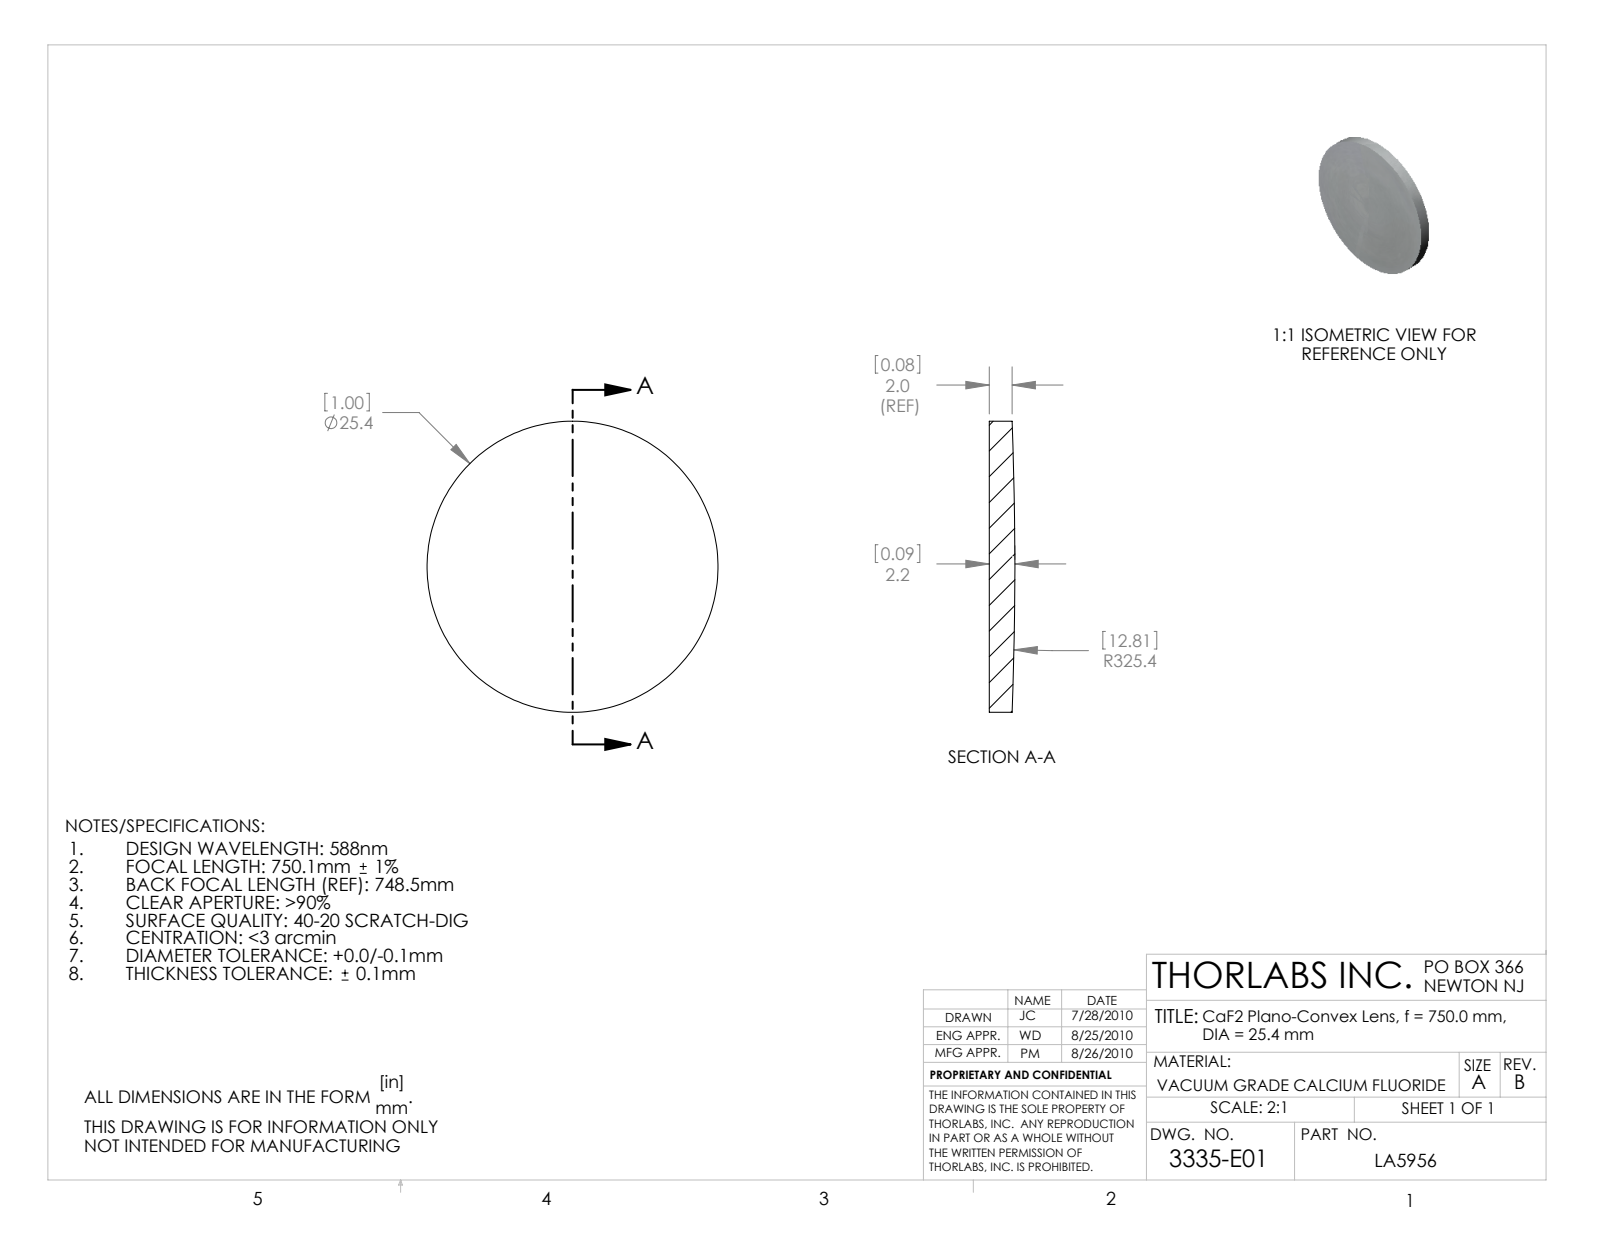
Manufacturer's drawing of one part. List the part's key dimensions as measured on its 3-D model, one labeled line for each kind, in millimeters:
Part name (STEP PRODUCT): 3335-E0W
STEP written by: SolidWorks 2009 (AUTOMOTIVE_DESIGN)
Units: millimetres
Bodies: 1 solid, 5 faces (1 planar, 2 cylindrical, 2 other)
Overall size (bounding box): 25.4 × 25.4 × 2.2
Volume: 1 100 mm³ · Surface area: 1 172 mm²
Round bosses / shafts (diameter × count): ⌀25.4 ×1
